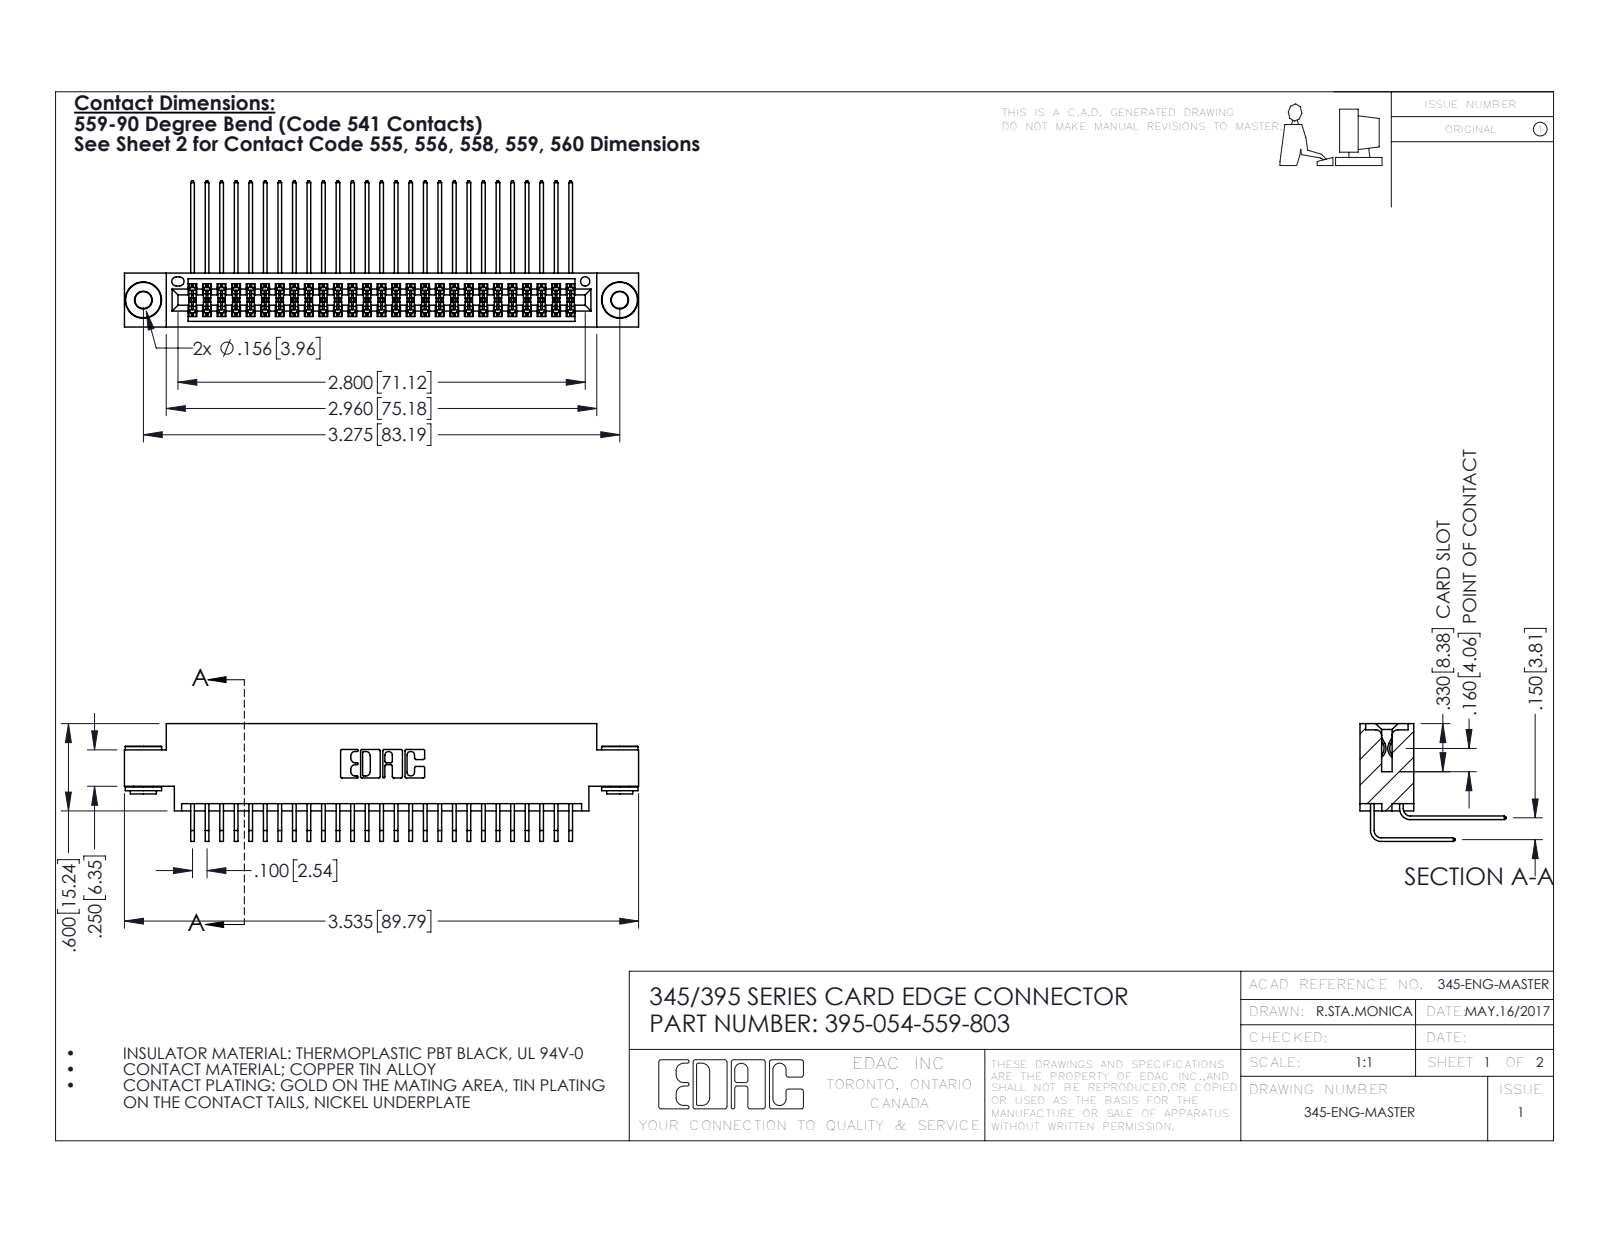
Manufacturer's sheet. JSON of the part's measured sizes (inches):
{"part_name": "345-292-001_558 559 Tail - 1; 345-292-001_559 Tail - 2; 345-250-002_345-250-002-102; 395-054-559-803 (+1 more)", "step_written_by": "SolidWorks 2016 (CONFIG_CONTROL_DESIGN)", "units": "inches", "bodies": {"solids": 57, "faces": 2976, "planar": 1984, "cylindrical": 984, "other": 8}, "overall_size": [3.535, 1.005, 0.809], "volume_in3": 0.537, "surface_area_in2": 22.52, "round_holes": [[0.116, 2], [0.156, 2], [0.064, 1]], "round_bosses_or_shafts": [[0.25, 2], [0.18, 2], [0.136, 2]], "partial_cylinders_radius": [[0.006, 81], [0.01, 22], [0.007, 6], [0.031, 6], [0.026, 3], [0.014, 2], [0.019, 2], [0.022, 2]], "face_to_face_distances": [0.072, 0.298, 0.37, 0.2, 0.098, 0.272, 0.025, 0.175, 0.15, 0.225], "hole_center_spacings": [0.27, 3.04, 3.275]}
